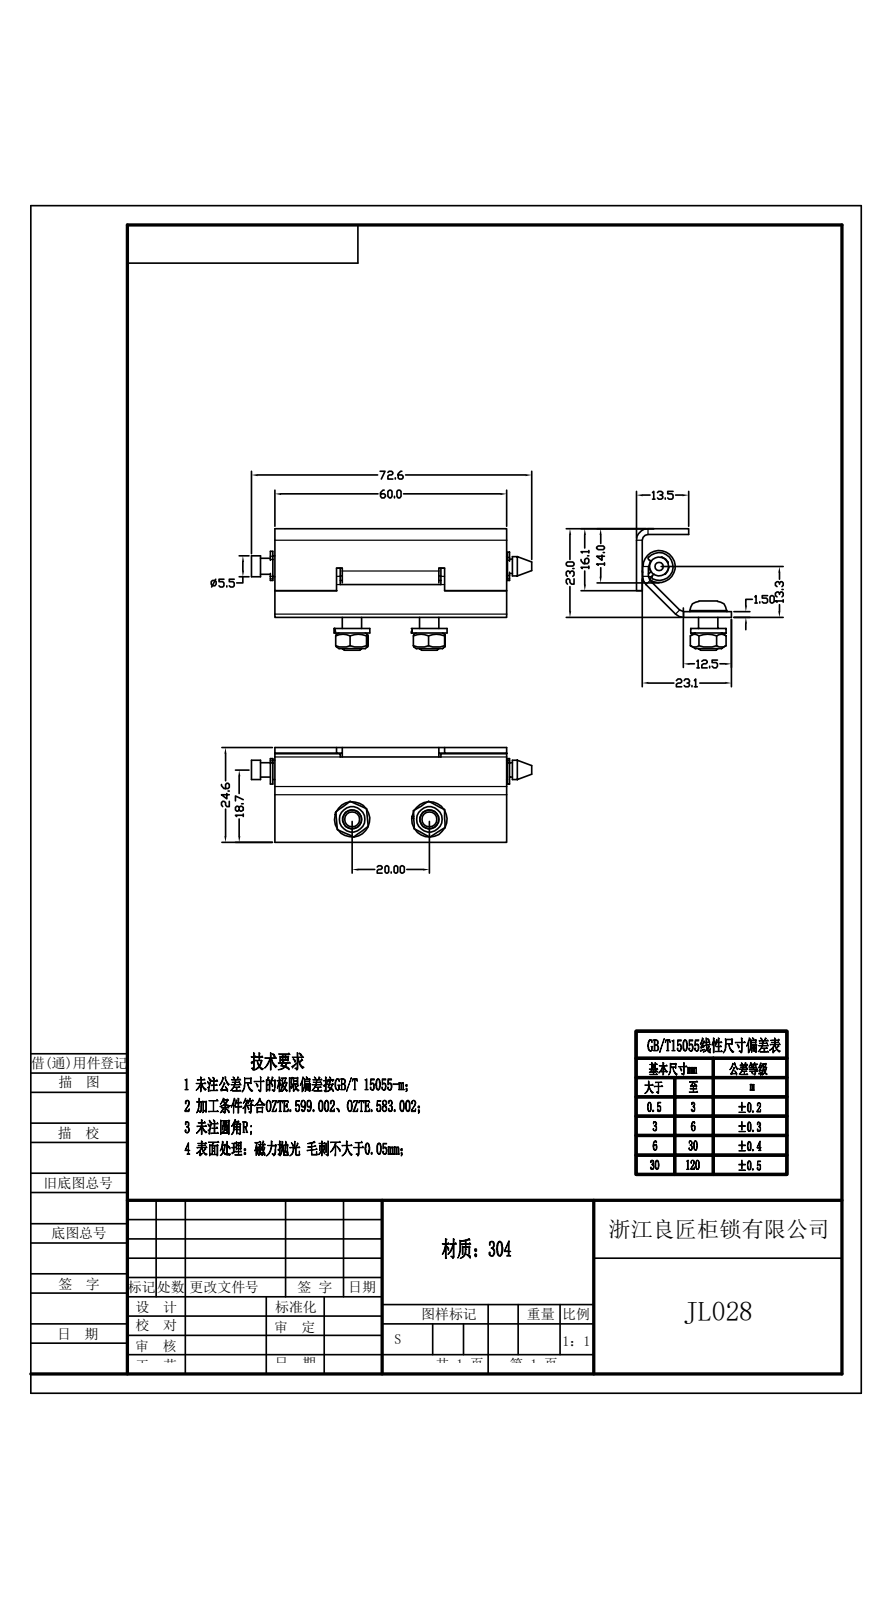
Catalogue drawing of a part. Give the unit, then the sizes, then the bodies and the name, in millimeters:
Units: millimetres
Overall size (bounding box): 72.67 × 31.55 × 24.58
Round holes (diameter × count): ⌀5 ×2, ⌀5.5 ×1
Round bosses / shafts (diameter × count): ⌀9.5 ×2, ⌀9.2 ×2, ⌀8.5 ×1, ⌀6.06 ×1, ⌀4.95 ×1, ⌀4.2 ×1, ⌀3.7 ×1
Partial cylindrical surfaces — rounded edges, fillets, slot ends (radius × count): R1 ×6, R1.5 ×4, R2.55 ×4, R3 ×3, R2.12 ×1, R2.5 ×1, R3.77 ×1
Main face-to-face distances: 1.5, 21.57, 23.07, 20.07, 4.01, 5.51, 25.58, 27.08, 11.03, 7.02
Hole centre spacings: 20
Volume: 7 409 mm³ · Surface area: 12 114 mm²
Bodies: 12 solids, 223 faces (115 planar, 78 cylindrical, 30 other)
STEP written by: Rhino 8.5 (CONFIG_CONTROL_DESIGN)
